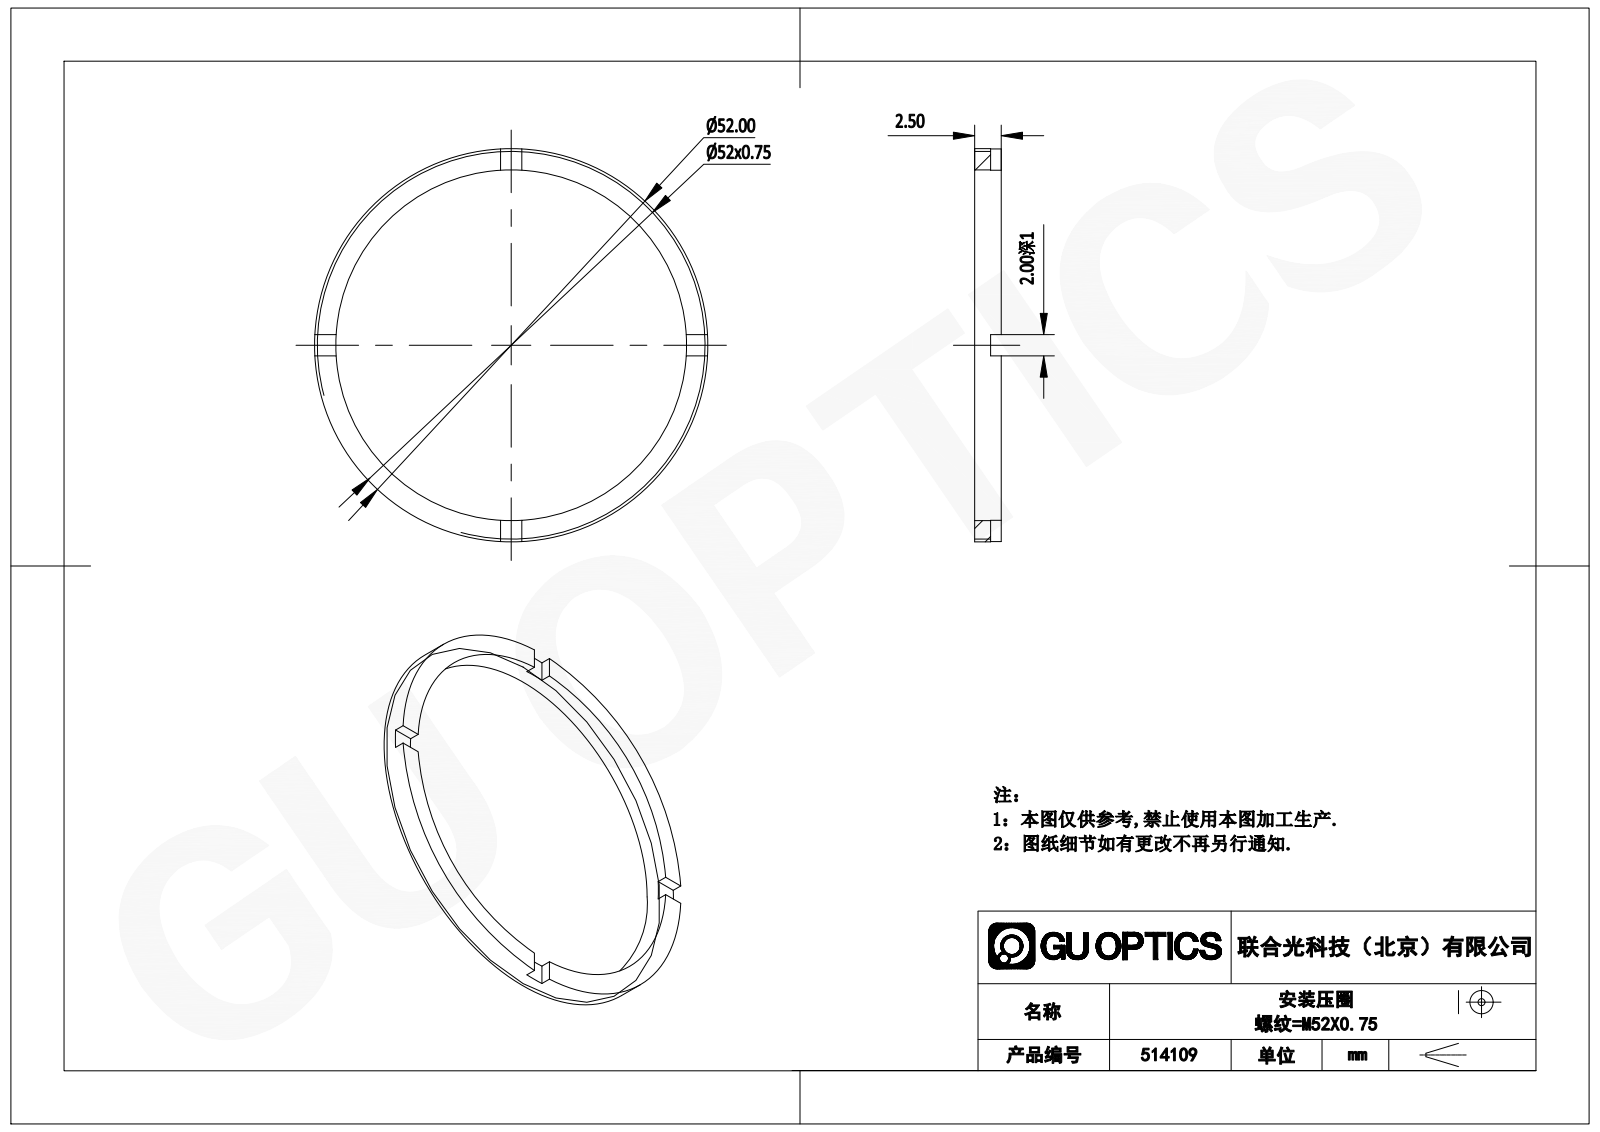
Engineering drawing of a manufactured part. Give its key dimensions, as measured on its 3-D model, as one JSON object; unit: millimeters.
{"part_name": "514109", "step_written_by": "SolidWorks 2020 (CONFIG_CONTROL_DESIGN)", "units": "millimeters", "bodies": {"solids": 1, "faces": 21, "planar": 17, "cylindrical": 4, "other": 0}, "overall_size": [52, 52, 2.5], "volume_mm3": 952, "surface_area_mm2": 1559, "round_holes": [[47, 1]], "round_bosses_or_shafts": [[52, 1]], "face_to_face_distances": [2.5, 1.5, 1, 2]}
